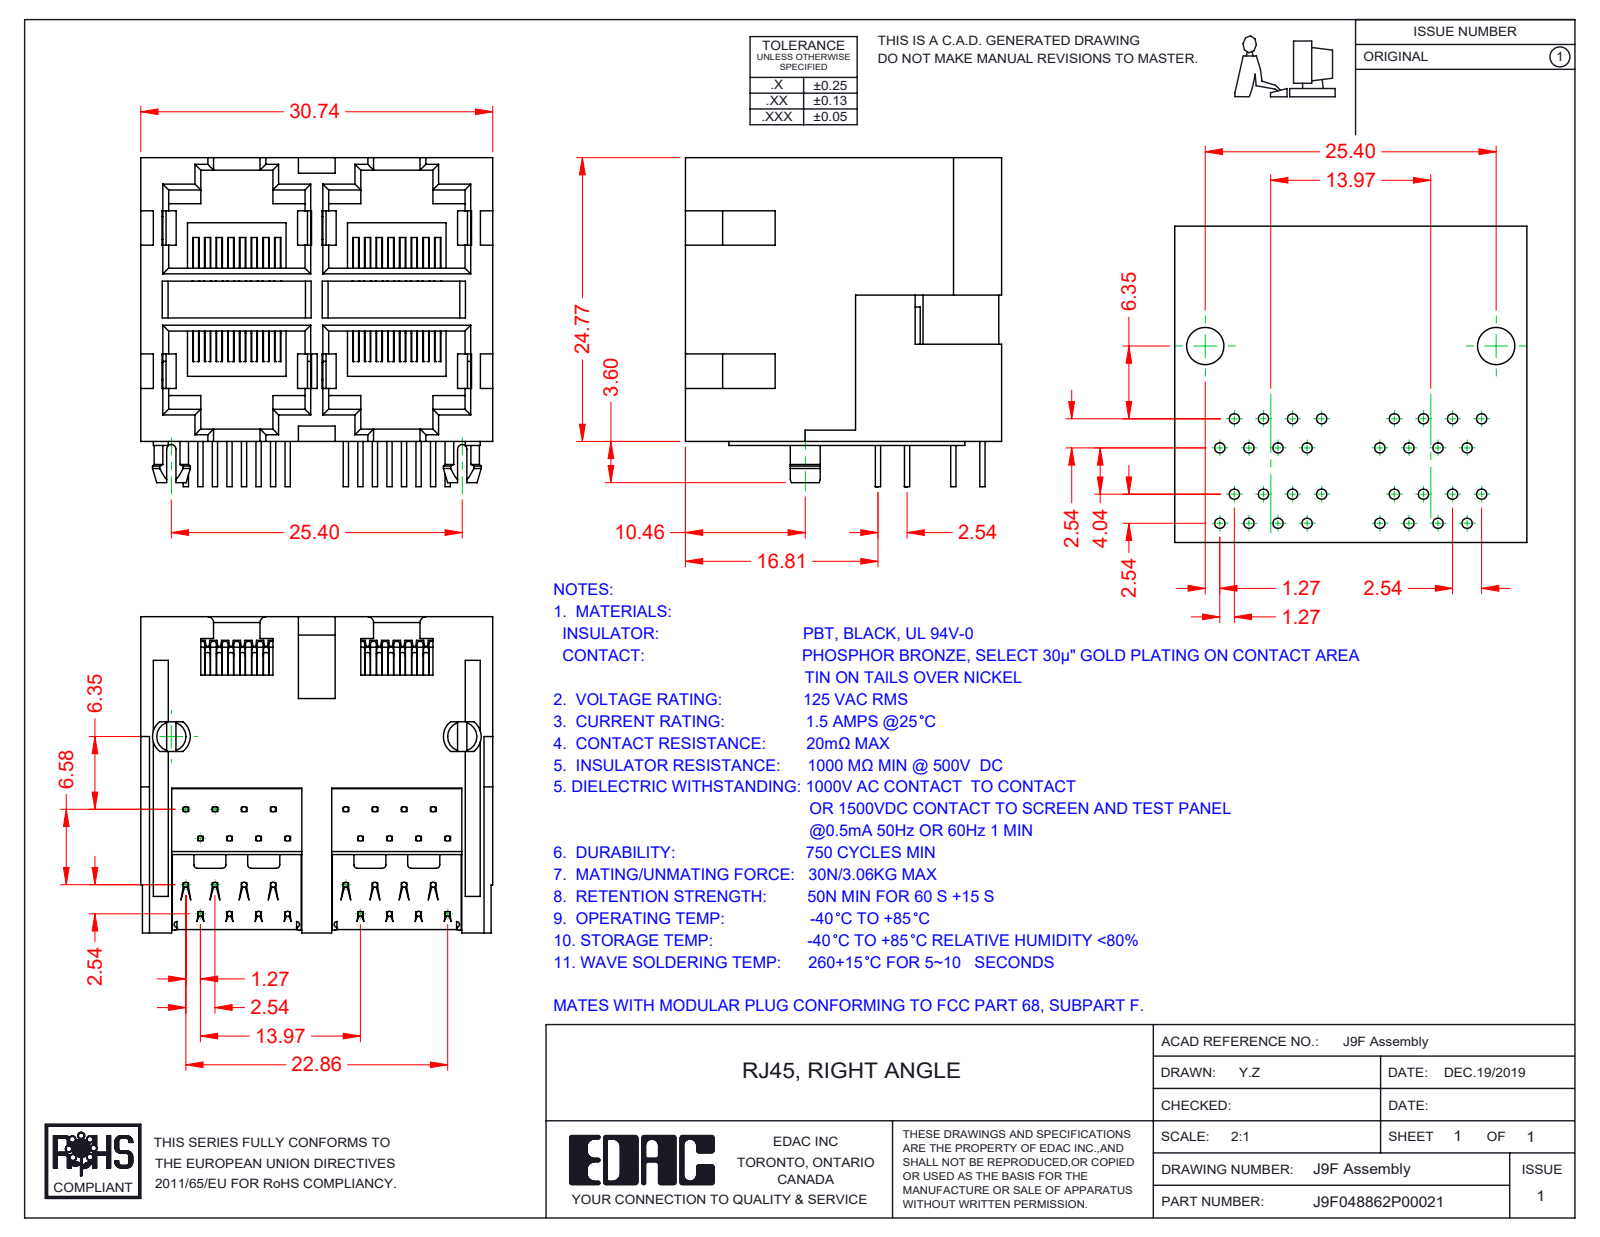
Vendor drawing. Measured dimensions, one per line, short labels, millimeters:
name: 9F Contacts Upper; RJ9F048862P00021; 9F Contact Lock Upper; 9F Contacts Lower (+2 more)
written by: SolidWorks 2016 (CONFIG_CONTROL_DESIGN)
unit: mm
bodies: 37 solids, 2810 faces (1899 planar, 557 cylindrical, 354 other)
size: 30.74 × 28.71 × 27.6
volume: 11 763 mm³; area: 19 774 mm²
bosses: 144× ⌀0.46
rounds: 63× R0.2, 25× R0.5, 9× R0.3, 4× R0.25, 2× R0.4, 2× R0.45, 2× R1.5, 2× R1.65
face distances: 13.97, 1, 0.35, 12.7, 15, 13.05, 11.98, 1.05, 13.62, 5.5
